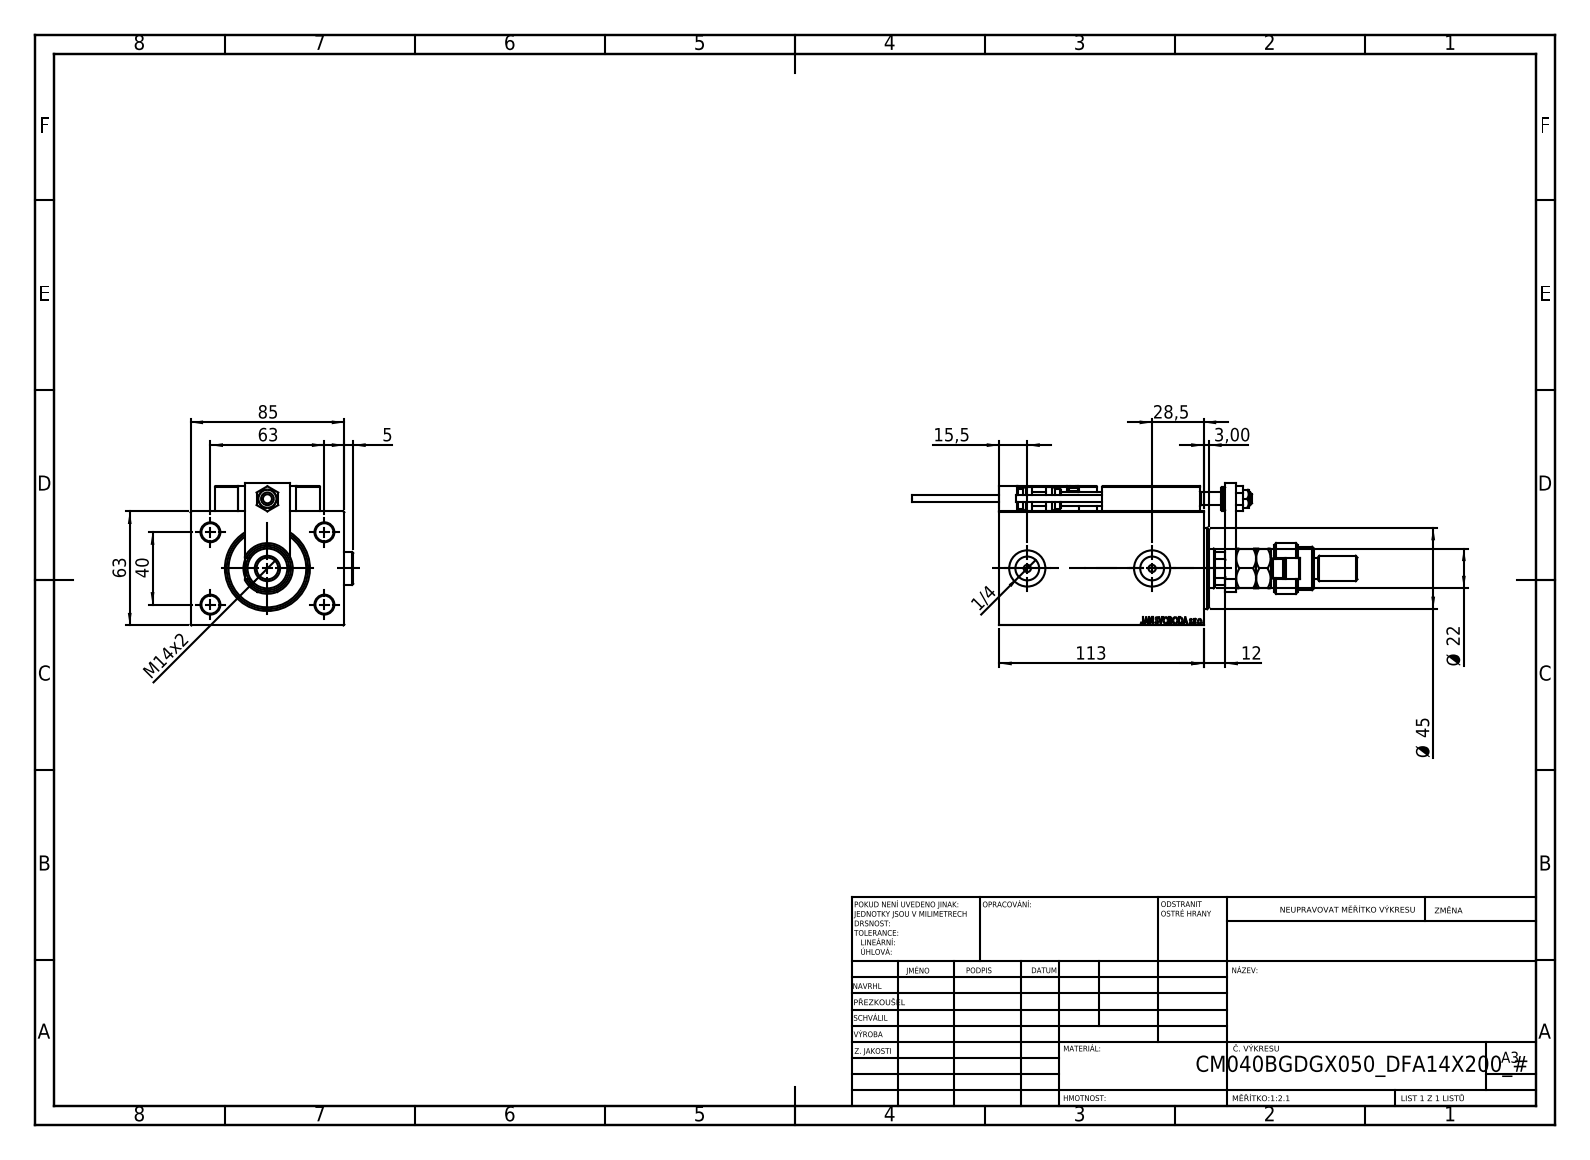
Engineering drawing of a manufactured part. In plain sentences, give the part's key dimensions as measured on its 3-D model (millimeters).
The part is named "ZARAZKA; Block; X_Y_DFA; NUT_D12 (+8 more)". Its 3-D file was written by "SolidWorks 2019 (CONFIG_CONTROL_DESIGN)". It is 28 solids with 1457 faces: 623 planar, 213 cylindrical and 621 other. Overall it measures 246 by 89.9 by 78.5 millimeters. Its volume is 619 536 cubic millimeters and its surface area 118 381 square millimeters. Round holes: 6 of diameter 4, 5 of diameter 8, 4 of diameter 3.2, 4 of diameter 10, 2 of diameter 5, 2 of diameter 13.16, 2 of diameter 20, 1 of diameter 7, 1 of diameter 12.5, 1 of diameter 16.5, 1 of diameter 22, 1 of diameter 25.5. Round bosses or shafts: 3 of diameter 18, 2 of diameter 11, 2 of diameter 5, 2 of diameter 3.8, 1 of diameter 28, 1 of diameter 24, 1 of diameter 14, 1 of diameter 13. Partial cylindrical surfaces (rounded edges, fillets, slot ends): 30 of radius 0.3, 2 of radius 3, 1 of radius 9.75, 1 of radius 10.5. The main face-to-face distances are 63, 85, 12, 101, 113, 14, 77, 30, 18, 3. The hole center spacings are 37.31, 11.37, 20, 29.59, 29.69, 36.06, 36.53, 40.
